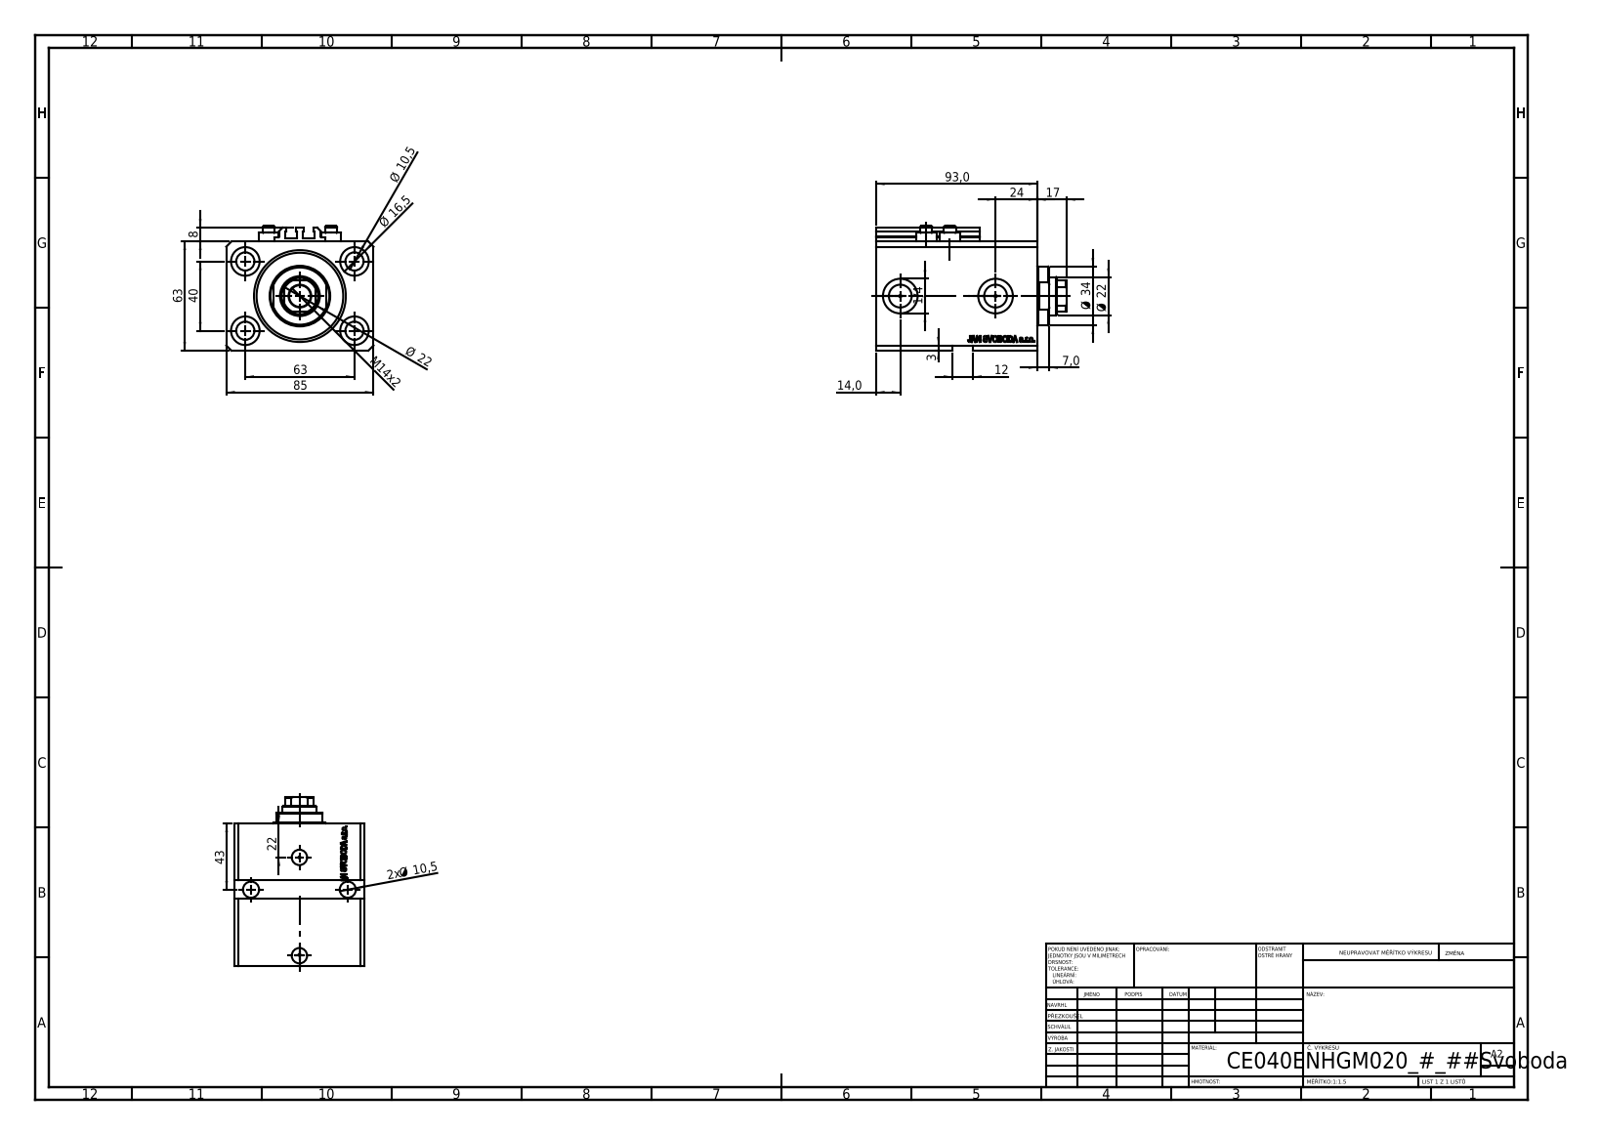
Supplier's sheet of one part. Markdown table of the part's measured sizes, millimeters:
| quantity | value |
| --- | --- |
| part name | V250CE_VC_E; V250CE_E_Body; ALLEN BOLT V250CE; V250CE_C_VCP |
| STEP written by | SolidWorks 2019 (CONFIG_CONTROL_DESIGN) |
| units | millimeters |
| bodies | 8 solids, 1087 faces (535 planar, 126 cylindrical, 426 other) |
| overall size | 110 × 85 × 72 |
| volume | 437 253 mm³ |
| surface area | 95 786 mm² |
| round holes (diameter × count) | 10.5 × 6, 1.25 × 4, 4 × 4, 16.5 × 4, 10 × 2, 13.16 × 2, 20 × 2, 12.5 × 1, 22 × 1, 40 × 1, 53 × 1 |
| round bosses / shafts (diameter × count) | 11.6 × 4, 7 × 4, 34 × 1 |
| partial cylindrical surfaces (radius × count) | 0.2 × 10, 10.5 × 1 |
| main face-to-face distances | 63, 85, 93, 17, 76, 11.4, 64.6, 81.6, 3, 65 |
| hole center spacings | 37.31, 63, 13.6, 15.4, 24.96, 28.02, 28.43, 33.62 |
